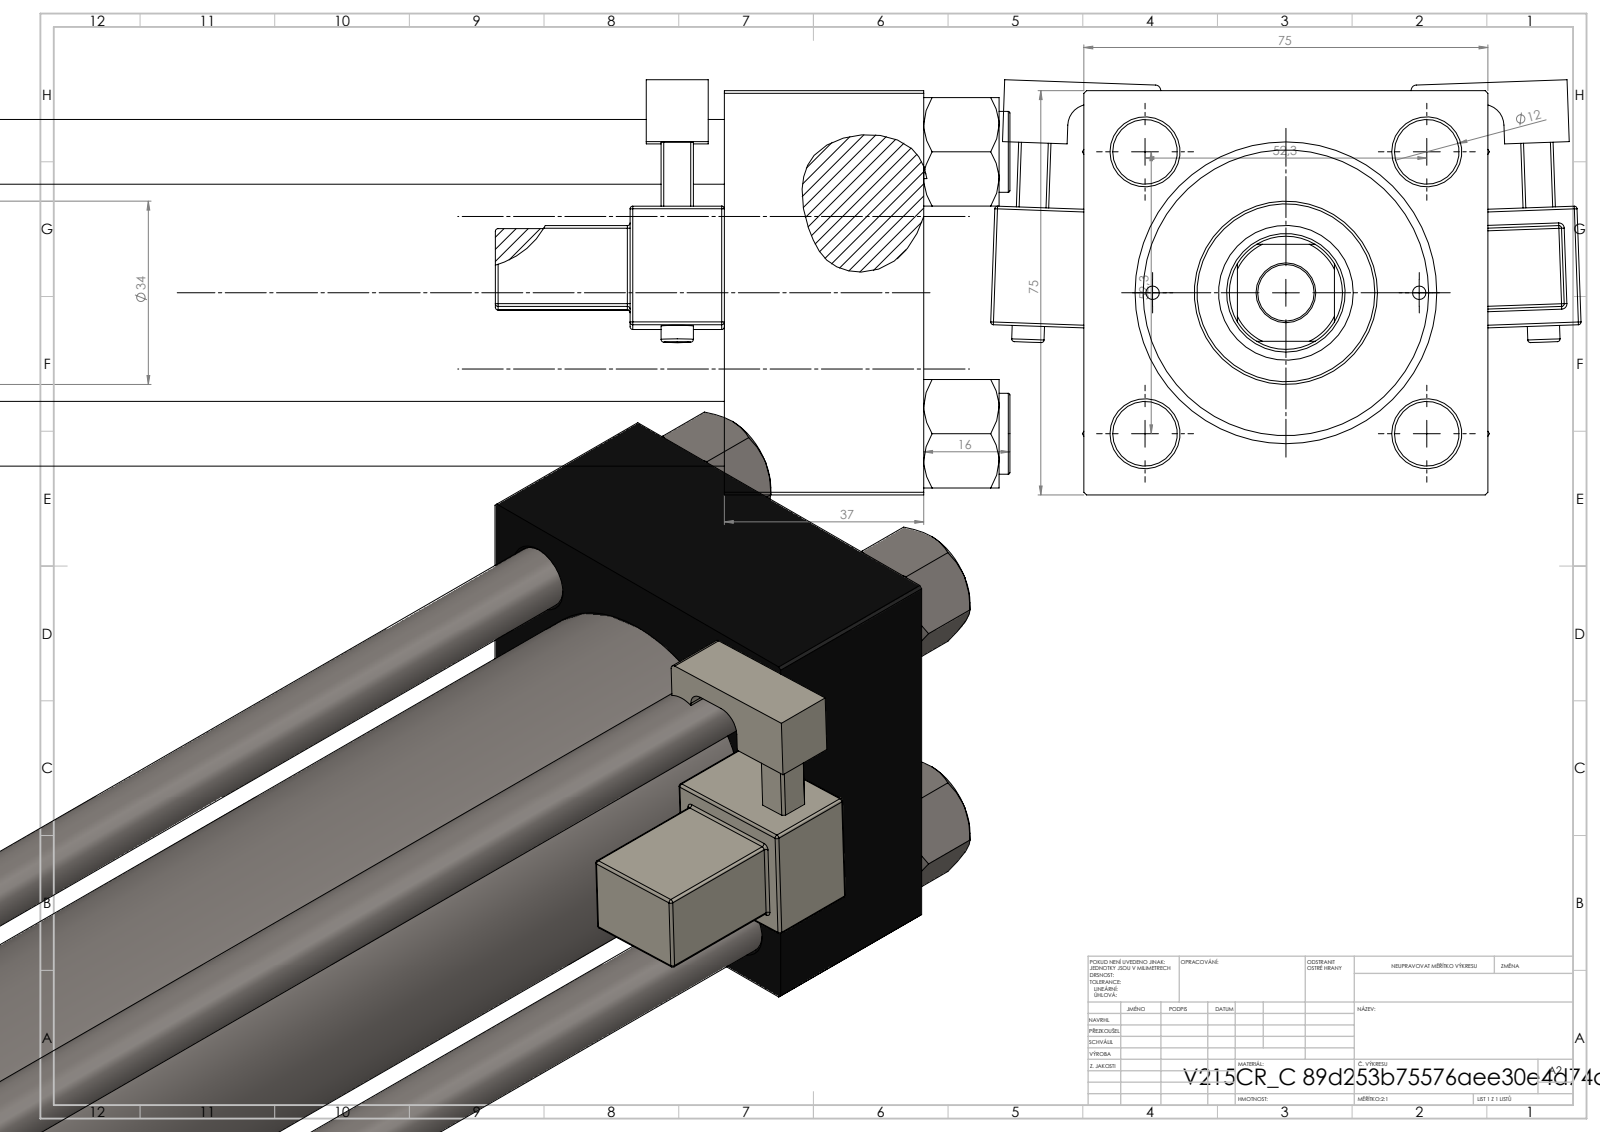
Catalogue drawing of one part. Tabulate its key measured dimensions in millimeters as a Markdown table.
| quantity | value |
| --- | --- |
| part name | NUT_M5_C; V215CR_VCP_C; V215CR_MSU; V215CR_C_Body (+2 more) |
| STEP written by | SolidWorks 2019 (CONFIG_CONTROL_DESIGN) |
| units | millimeters |
| bodies | 13 solids, 1308 faces (586 planar, 150 cylindrical, 572 other) |
| overall size | 575 × 109.57 × 77.03 |
| volume | 1 204 000 mm³ |
| surface area | 369 742 mm² |
| round holes (diameter × count) | 12 × 4, 2.5 × 2, 7 × 2, 20.96 × 2, 30 × 2, 10.5 × 1, 22 × 1, 25 × 1, 41 × 1, 50 × 1, 53 × 1 |
| round bosses / shafts (diameter × count) | 15 × 4, 6 × 2, 56 × 1, 34 × 1 |
| partial cylindrical surfaces (radius × count) | 0.5 × 48, 1 × 2, 2.5 × 2, 4 × 2, 10.5 × 1 |
| main face-to-face distances | 75, 37, 534, 497, 475, 438, 59, 505.3, 468.3, 30.3 |
| hole center spacings | 26.19, 36.98, 52.3, 57.22, 24.75, 73.96, 49.5, 473.5 |
